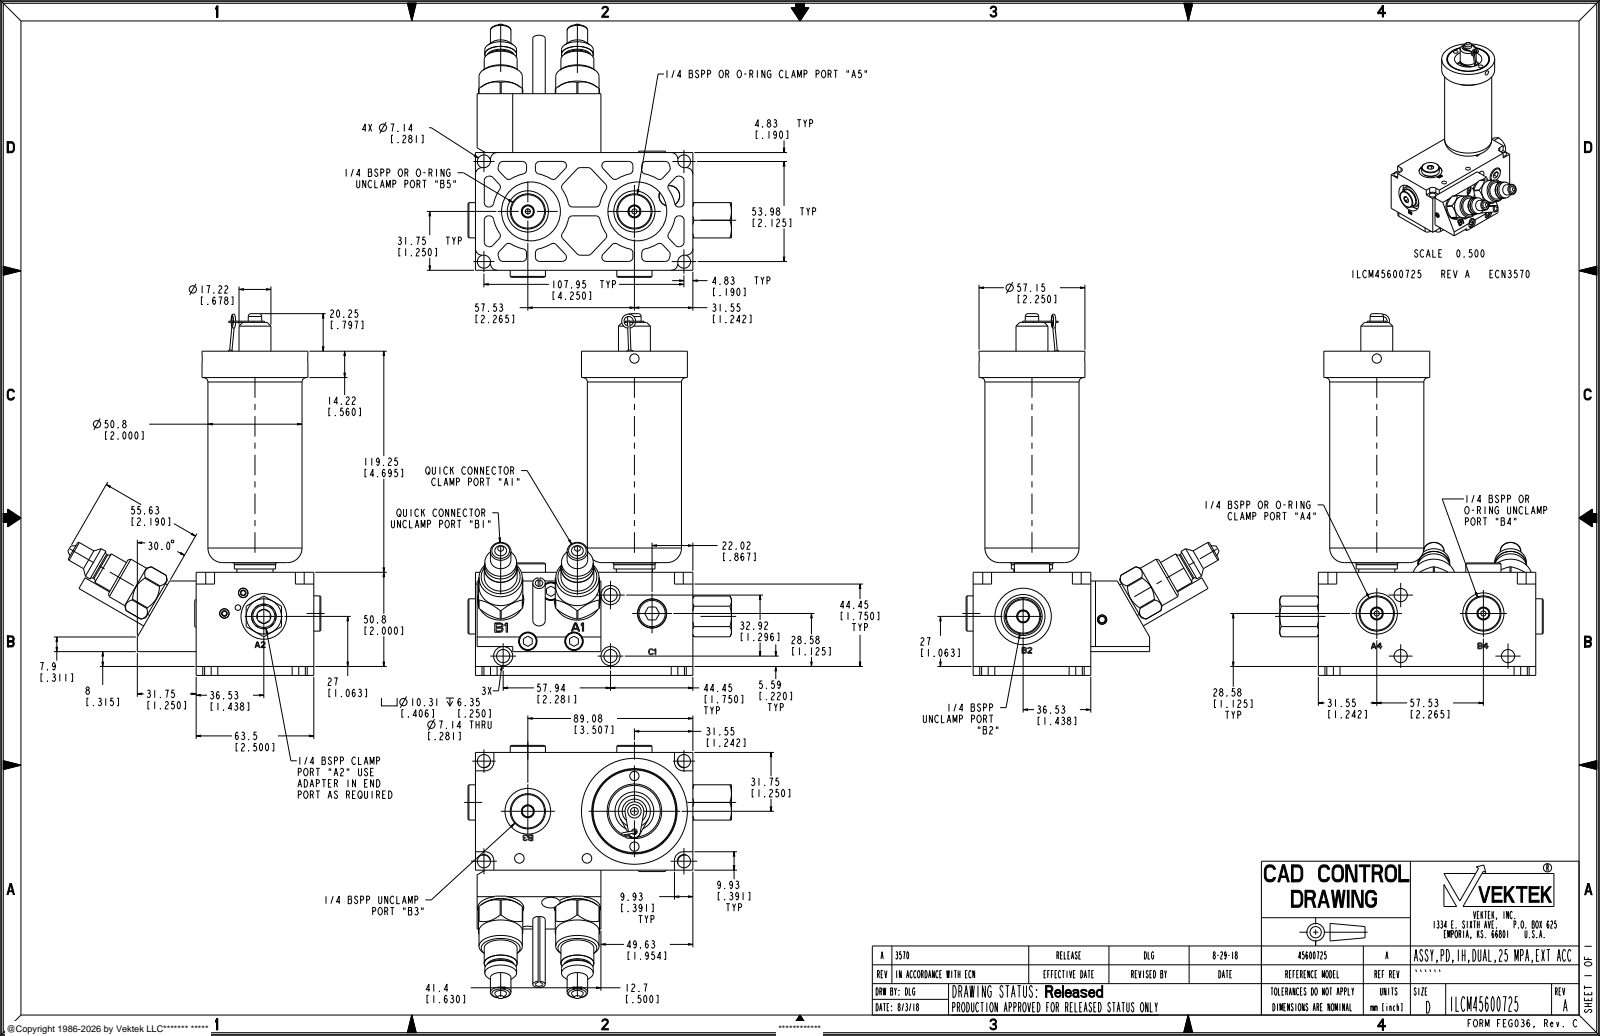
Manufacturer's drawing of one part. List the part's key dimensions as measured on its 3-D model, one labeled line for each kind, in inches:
Part name (STEP PRODUCT): ILCM45600725; 45600511; 30871966
STEP written by: PRO/ENGINEER BY PARAMETRIC TECHNOLOGY CORPORATION, 2013320 (CONFIG_CONTROL_DESIGN)
Units: inches
Bodies: 6 solids, 1662 faces (999 planar, 345 cylindrical, 318 other)
Overall size (bounding box): 7.682 × 5.599 × 5.376
Volume: 37.32 in³ · Surface area: 197 in²
Round holes (diameter × count): ⌀0.281 ×7, ⌀0.875 ×5, ⌀0.197 ×3, ⌀0.391 ×3, ⌀0.406 ×3, ⌀0.97 ×3, ⌀0.079 ×2, ⌀0.118 ×2, ⌀0.123 ×2, ⌀0.202 ×2, ⌀0.203 ×2, ⌀0.515 ×2
Round bosses / shafts (diameter × count): ⌀0.748 ×5, ⌀0.375 ×3, ⌀0.92 ×2, ⌀0.75 ×2, ⌀0.699 ×2, ⌀0.675 ×2, ⌀0.585 ×2, ⌀0.437 ×2
Partial cylindrical surfaces — rounded edges, fillets, slot ends (radius × count): R0.09 ×68, R0.14 ×12, R0.187 ×4, R0.125 ×2, R0.536 ×2, R0.812 ×2, R0.108 ×1, R0.166 ×1
Main face-to-face distances: 2, 2.5, 0.19, 2.19, 4.62, 0.315, 0.505, 1.685, 5.868, 1.5
Hole centre spacings: 0.75, 0.752, 0.755, 0.956, 1.157, 2.125, 2.198, 2.265
